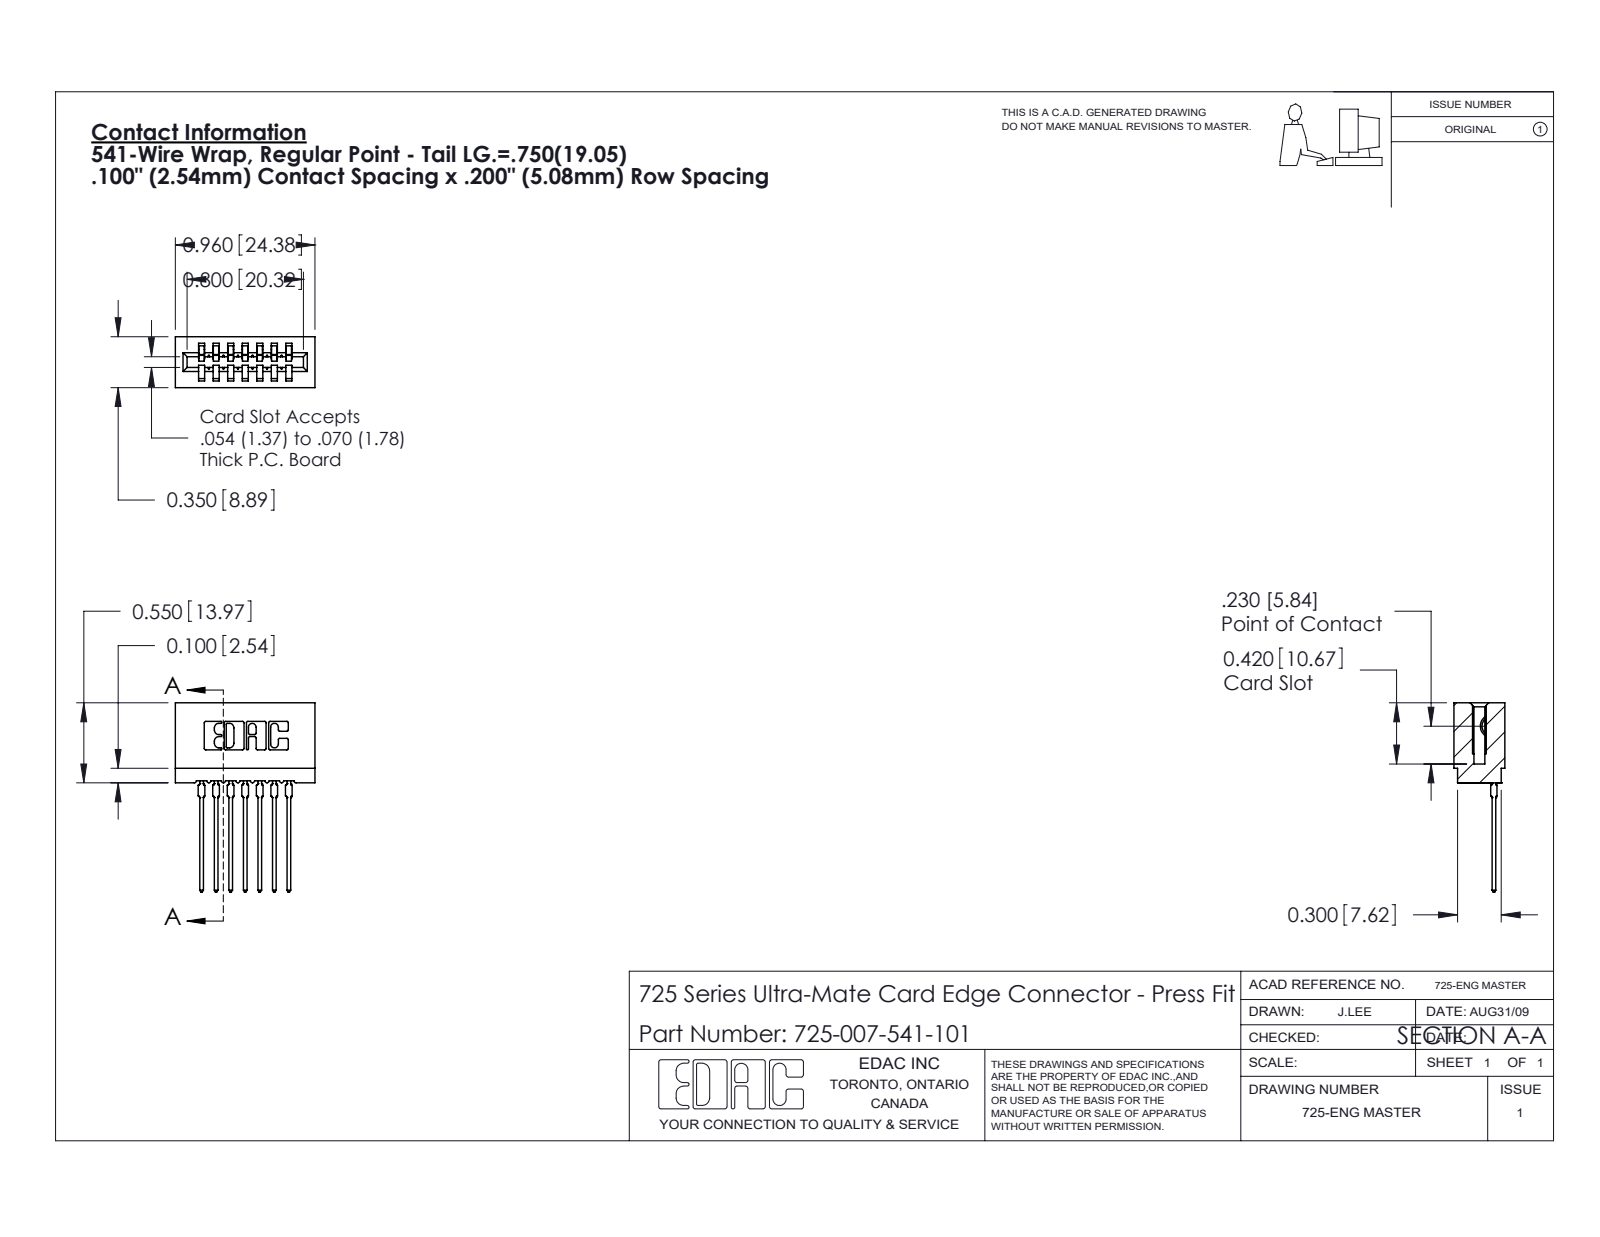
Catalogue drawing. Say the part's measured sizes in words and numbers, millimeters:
The part is named "725-007-541-101; 725 Part_Insulator Option - 01; 745-292-001_541". Its 3-D file was written by "SolidWorks 2020 (CONFIG_CONTROL_DESIGN)". It is 8 solids with 879 faces: 524 planar, 173 cylindrical and 182 other. Overall it measures 33 by 24.4 by 8.9 millimeters. Its volume is 2 080 cubic millimeters and its surface area 3 497 square millimeters. Partial cylindrical surfaces (rounded edges, fillets, slot ends): 22 of radius 0.3, 14 of radius 0.4, 14 of radius 0.5, 6 of radius 0.2, 6 of radius 0.8, 4 of radius 0.1, 4 of radius 0.3, 3 of radius 0.7. The main face-to-face distances are 2.5, 5.1, 7.6, 1.1, 10.2, 3.6, 1.5, 6.1, 4, 12.7.
